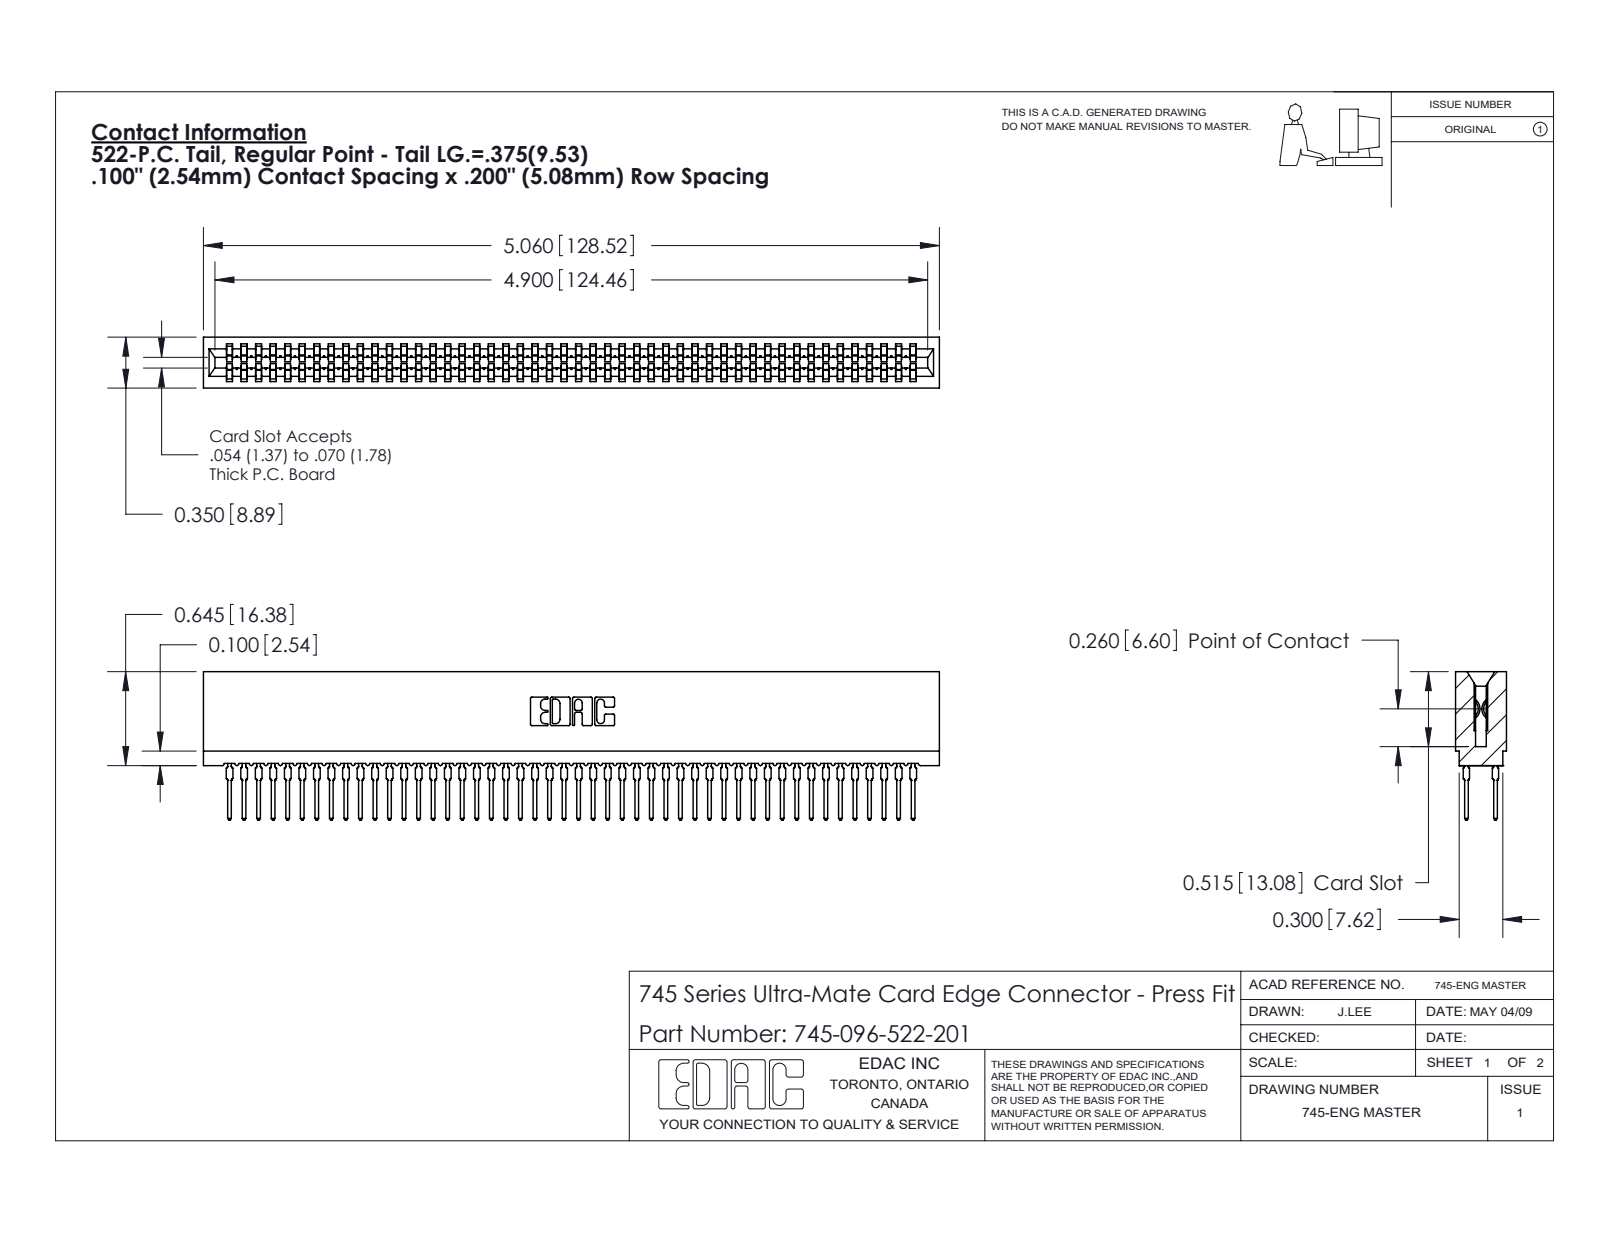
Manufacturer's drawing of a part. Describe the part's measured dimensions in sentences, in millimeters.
The part is named "745-096-522-201; 745 Part_Insulator Option - 01; 745-292-001_522". Its 3-D file was written by "SolidWorks 2020 (CONFIG_CONTROL_DESIGN)". It is 97 solids with 8687 faces: 4471 planar, 1720 cylindrical and 2496 other. Overall it measures 128.5 by 25.9 by 8.9 millimeters. Its volume is 11 600 cubic millimeters and its surface area 24 140 square millimeters. Partial cylindrical surfaces (rounded edges, fillets, slot ends): 192 of radius 0.5, 96 of radius 0.4, 22 of radius 0.3, 8 of radius 0.1, 8 of radius 0.3, 6 of radius 0.2, 6 of radius 0.8, 3 of radius 0.7. The main face-to-face distances are 8.9, 1.6, 7.3, 5.1, 1.1, 7.7, 0.5, 6.2, 3.5, 5.4.
